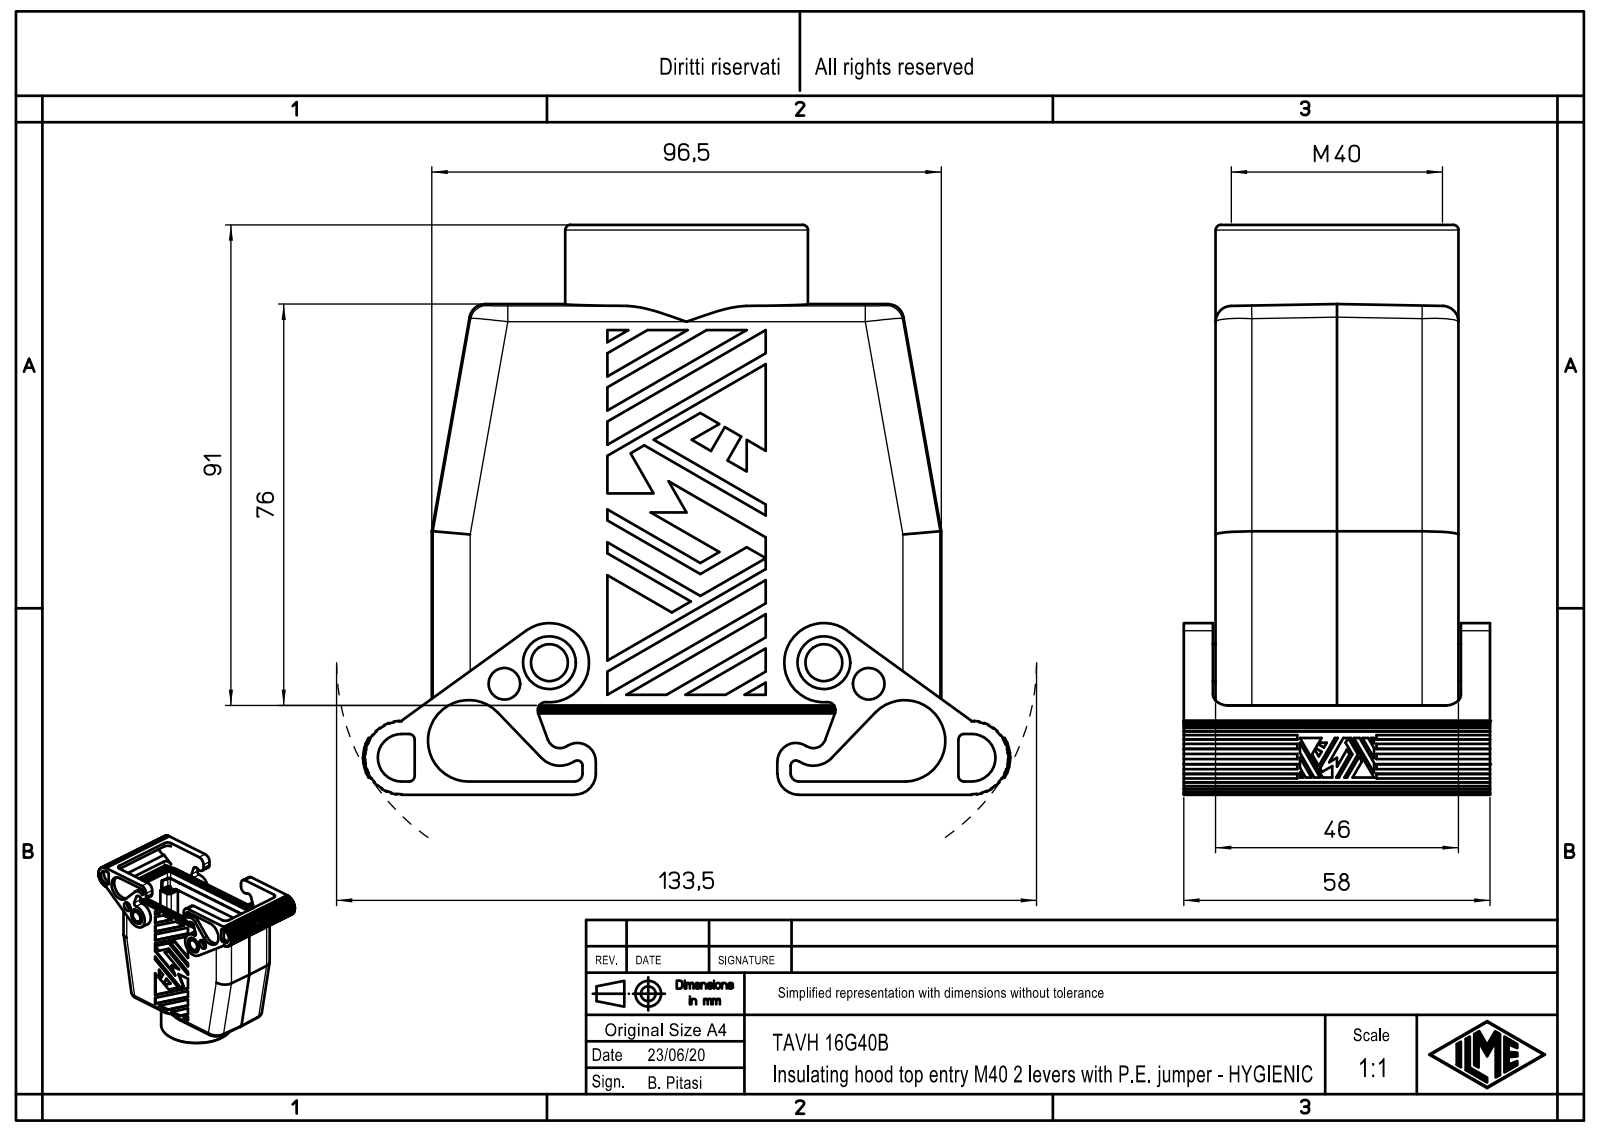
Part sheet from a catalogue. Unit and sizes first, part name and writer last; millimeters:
Units: millimetres
Overall size (bounding box): 122.6 × 107.9 × 58
Round holes (diameter × count): ⌀3.5 ×4, ⌀5.12 ×4, ⌀6.5 ×4, ⌀6 ×2, ⌀10 ×2, ⌀34 ×1, ⌀40 ×1
Round bosses / shafts (diameter × count): ⌀7 ×2, ⌀46 ×1
Partial cylindrical surfaces — rounded edges, fillets, slot ends (radius × count): R1.5 ×16, R3 ×10, R7 ×10, R1 ×8, R1.81 ×8, R2 ×8, R1.3 ×4, R1.6 ×4
Main face-to-face distances: 46, 0.5, 46.5, 1, 45.5, 2.5, 5.5, 6, 6.5, 51.5
Hole centre spacings: 41.03, 9.39, 27, 60.63, 77.5, 82.07, 52, 69
Volume: 150 601 mm³ · Surface area: 68 665 mm²
Bodies: 1 solid, 802 faces (536 planar, 238 cylindrical, 28 other)
Part name (STEP PRODUCT): TAVH_16G40B
STEP written by: Creo Elements/Direct Modeling 20.1B 02-Apr-2019 (C) Parametric Technology GmbH (AUTOMOTIVE_DESIGN)
